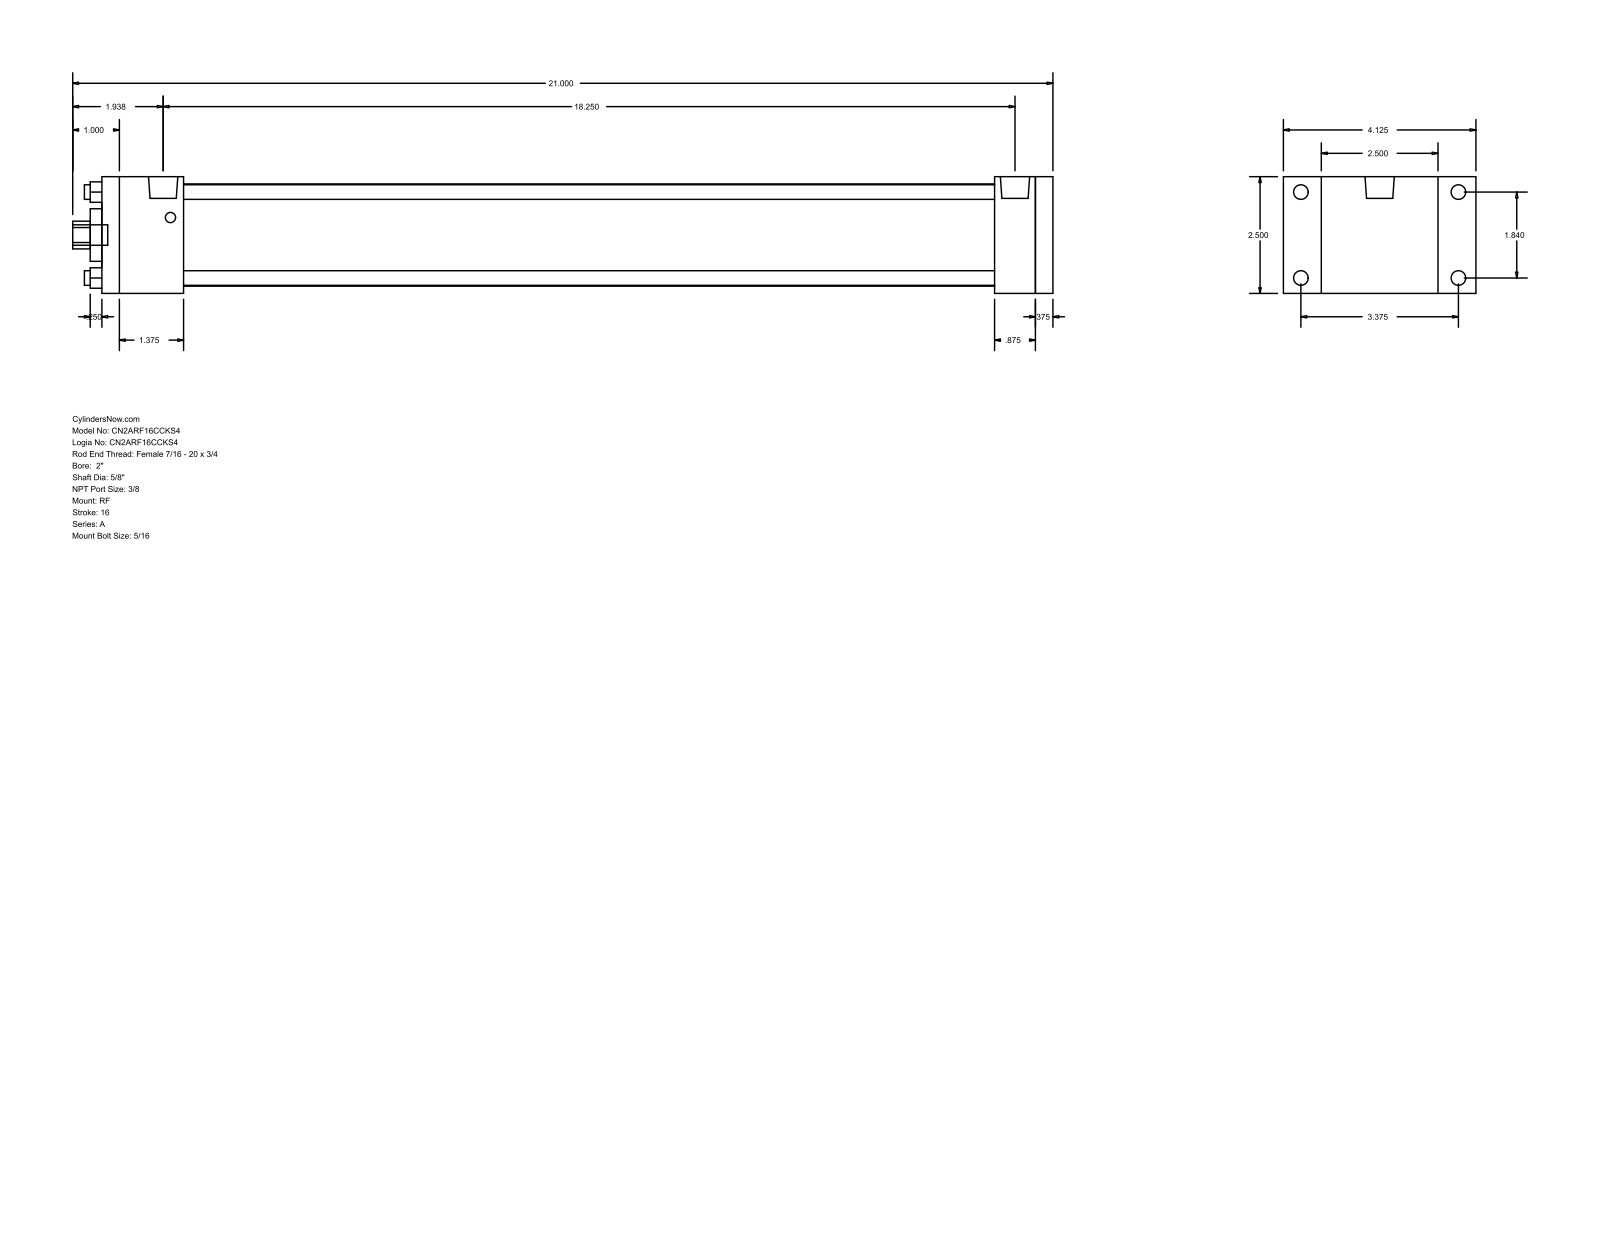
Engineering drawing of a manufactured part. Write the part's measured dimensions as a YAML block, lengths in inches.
part_name: "A_RF__0200_0.625"
step_written_by: "GSSL Pune (CONFIG_CONTROL_DESIGN)"
units: inches
bodies: {solids: 0, faces: 92, planar: 64, cylindrical: 28, other: 0}
overall_size: [21, 4.125, 2.5]
round_holes:
  - {diameter: 0.313, count: 4}
  - {diameter: 0.625, count: 1}
  - {diameter: 1.125, count: 1}
  - {diameter: 2.19, count: 1}
round_bosses_or_shafts:
  - {diameter: 0.313, count: 4}
  - {diameter: 0.219, count: 4}
  - {diameter: 0.627, count: 2}
  - {diameter: 0.437, count: 1}
partial_cylinders:
  - {radius: 0.297, count: 1}
face_to_face_distances: [2.5, 20.375, 0.375, 20, 1.75, 18.25, 18.625, 19.125, 17.375, 0.875]
hole_center_spacings: [1.301, 1.84, 2.602]
